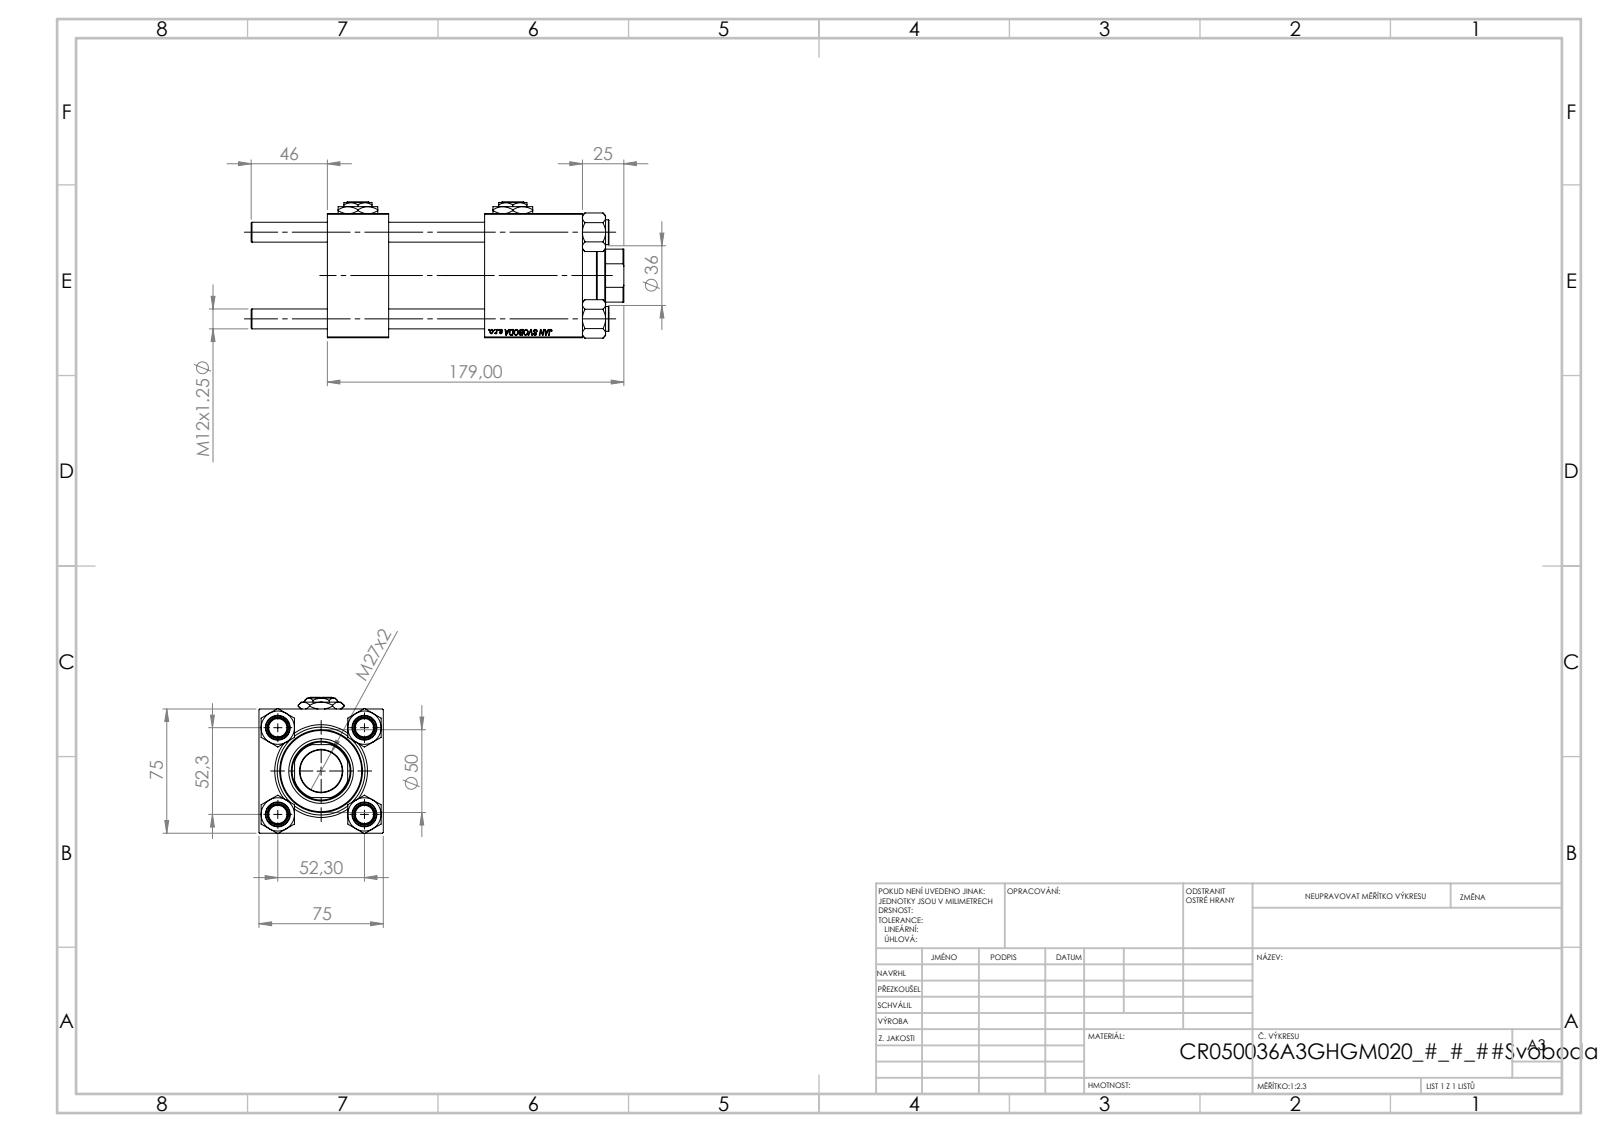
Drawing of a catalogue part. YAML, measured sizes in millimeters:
part_name: "NUT_M5; V215CR_VCP; V215CR_BODY_A; V215_VC_A (+2 more)"
step_written_by: "SolidWorks 2019 (CONFIG_CONTROL_DESIGN)"
units: millimeters
bodies: {solids: 13, faces: 1233, planar: 567, cylindrical: 88, other: 578}
overall_size: [225, 82.27, 75]
volume: 714043
surface_area: 176424
round_holes:
  - {diameter: 12, count: 4}
  - {diameter: 7, count: 2}
  - {diameter: 20.96, count: 2}
  - {diameter: 30, count: 2}
  - {diameter: 25.5, count: 1}
  - {diameter: 36, count: 1}
  - {diameter: 39, count: 1}
  - {diameter: 41, count: 1}
  - {diameter: 53, count: 1}
round_bosses_or_shafts:
  - {diameter: 15, count: 4}
  - {diameter: 56, count: 1}
  - {diameter: 50, count: 1}
partial_cylinders:
  - {radius: 17.5, count: 1}
face_to_face_distances: [75, 37, 95, 154, 117, 59, 58, 74.8, 125.3, 88.3]
hole_center_spacings: [36.98, 52.3, 73.96, 93.5]
